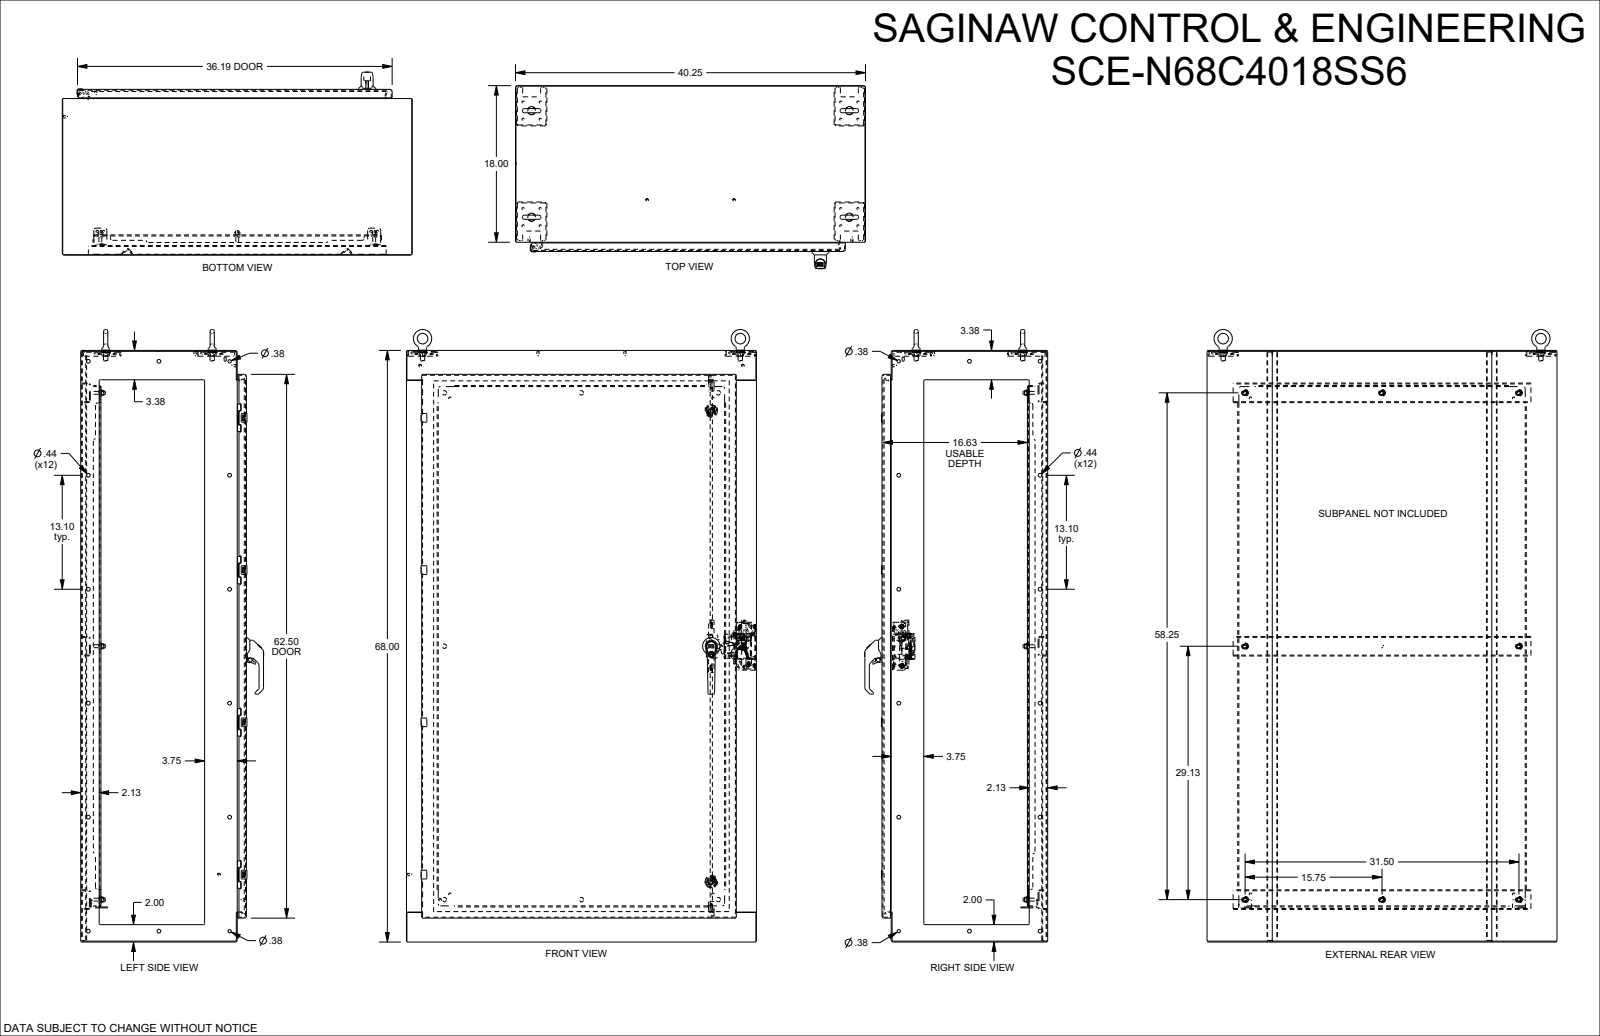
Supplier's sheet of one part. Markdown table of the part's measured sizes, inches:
| quantity | value |
| --- | --- |
| part name | SCE-N68C4018 |
| STEP written by | SolidWorks 2023 (AUTOMOTIVE_DESIGN) |
| units | inches |
| bodies | 55 solids, 5223 faces (1985 planar, 1988 cylindrical, 1250 other) |
| overall size | 70.423 × 40.25 × 21.038 |
| volume | 954.3 in³ |
| surface area | 18 113 in² |
| round holes (diameter × count) | 0.25 × 18, 0.437 × 12, 0.17 × 4, 0.256 × 4, 0.5 × 4, 0.875 × 4, 0.135 × 2, 0.138 × 2, 0.156 × 2, 0.177 × 2, 0.193 × 2, 0.195 × 2 |
| round bosses / shafts (diameter × count) | 1.012 × 4, 1 × 4, 0.73 × 4, 0.25 × 3, 1.4 × 2, 0.48 × 2, 0.341 × 2, 0.3 × 2 |
| partial cylindrical surfaces (radius × count) | 0.03 × 158, 0.131 × 144, 0.158 × 144, 0.015 × 130, 0.125 × 88, 0.02 × 83, 0.167 × 38, 0.062 × 36 |
| main face-to-face distances | 0.104, 18.954, 19.058, 18.85, 67.896, 17.896, 1.058, 0.104, 40.146, 67.792 |
| hole center spacings | 1.979, 1.4, 12.25, 13.1, 20.873, 2.799, 12.409, 26.2 |
